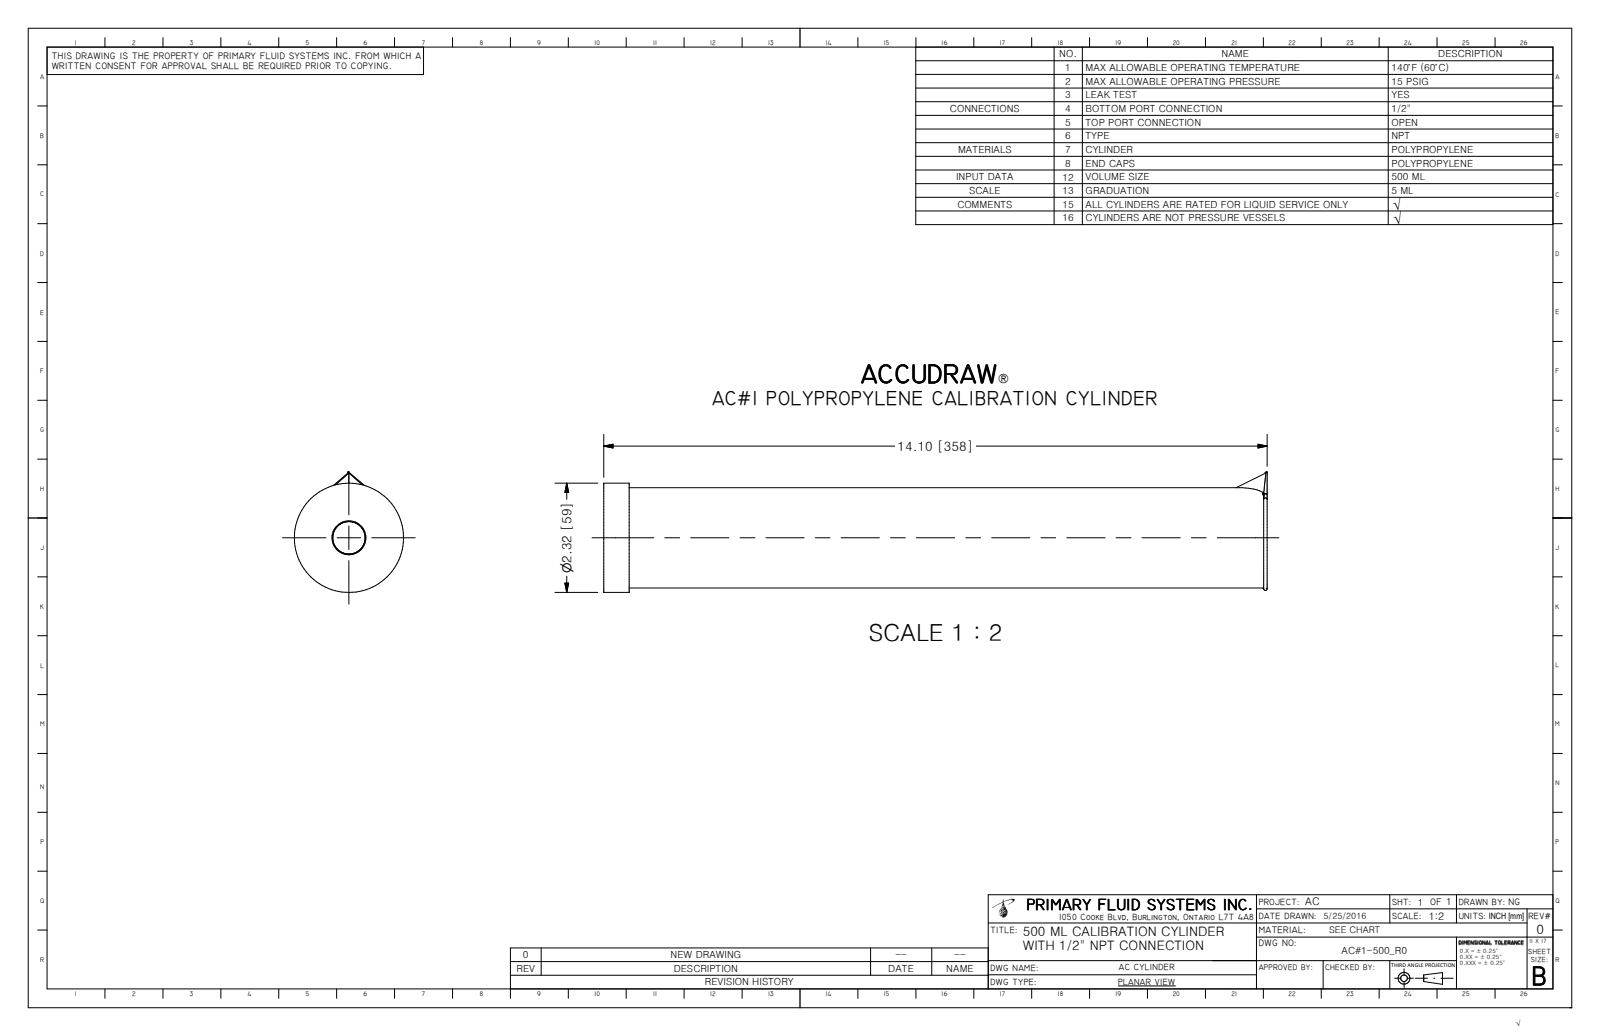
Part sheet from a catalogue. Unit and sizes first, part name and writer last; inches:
Units: inches
Overall size (bounding box): 14.099 × 2.553 × 2.32
Round holes (diameter × count): ⌀1.965 ×1
Round bosses / shafts (diameter × count): ⌀2.32 ×1, ⌀2.13 ×1, ⌀1.85 ×1
Main face-to-face distances: 0.75, 0.54, 0.21, 14.1, 13.559, 13.35, 14.022, 13.481, 13.272, 0.078
Volume: 9.77 in³ · Surface area: 190.7 in²
Bodies: 2 solids, 24 faces (10 planar, 4 cylindrical, 10 other)
Part name (STEP PRODUCT): AC#1-500_R0; AC-2B-500; AC#1-500-TUBE
STEP written by: Autodesk Inventor 2009 (AUTOMOTIVE_DESIGN)
